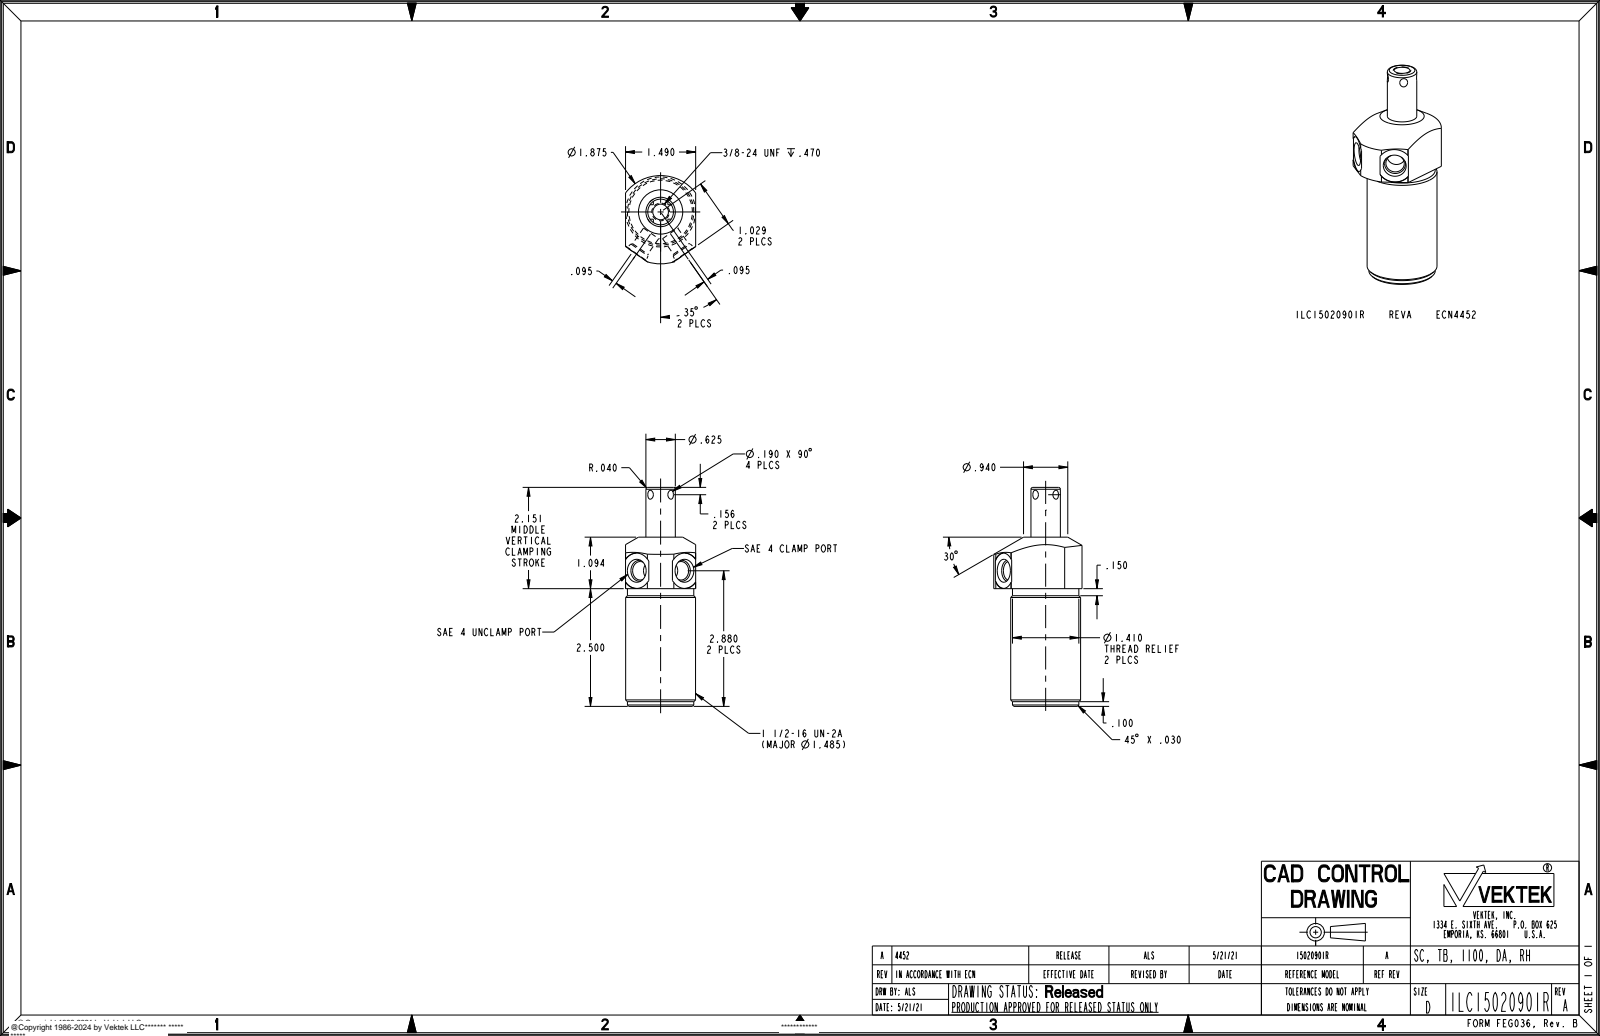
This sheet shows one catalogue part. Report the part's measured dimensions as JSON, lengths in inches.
{"part_name": "ILC15020901R", "step_written_by": "PRO/ENGINEER BY PARAMETRIC TECHNOLOGY CORPORATION, 2013320 (CONFIG_CONTROL_DESIGN)", "units": "inches", "bodies": {"solids": 1, "faces": 69, "planar": 15, "cylindrical": 26, "other": 28}, "overall_size": [4.651, 1.875, 1.49], "volume_in3": 6.804, "surface_area_in2": 26.22, "round_holes": [[0.392, 2], [0.332, 1]], "round_bosses_or_shafts": [[1.485, 1], [1.41, 1], [0.625, 1], [0.375, 1]], "partial_cylinders_radius": [[0.375, 2], [0.937, 1]], "face_to_face_distances": [1.49, 2.5, 3.594, 1.094, 0.53, 4.651, 2.151, 1.057, 0.54, 0.54]}
